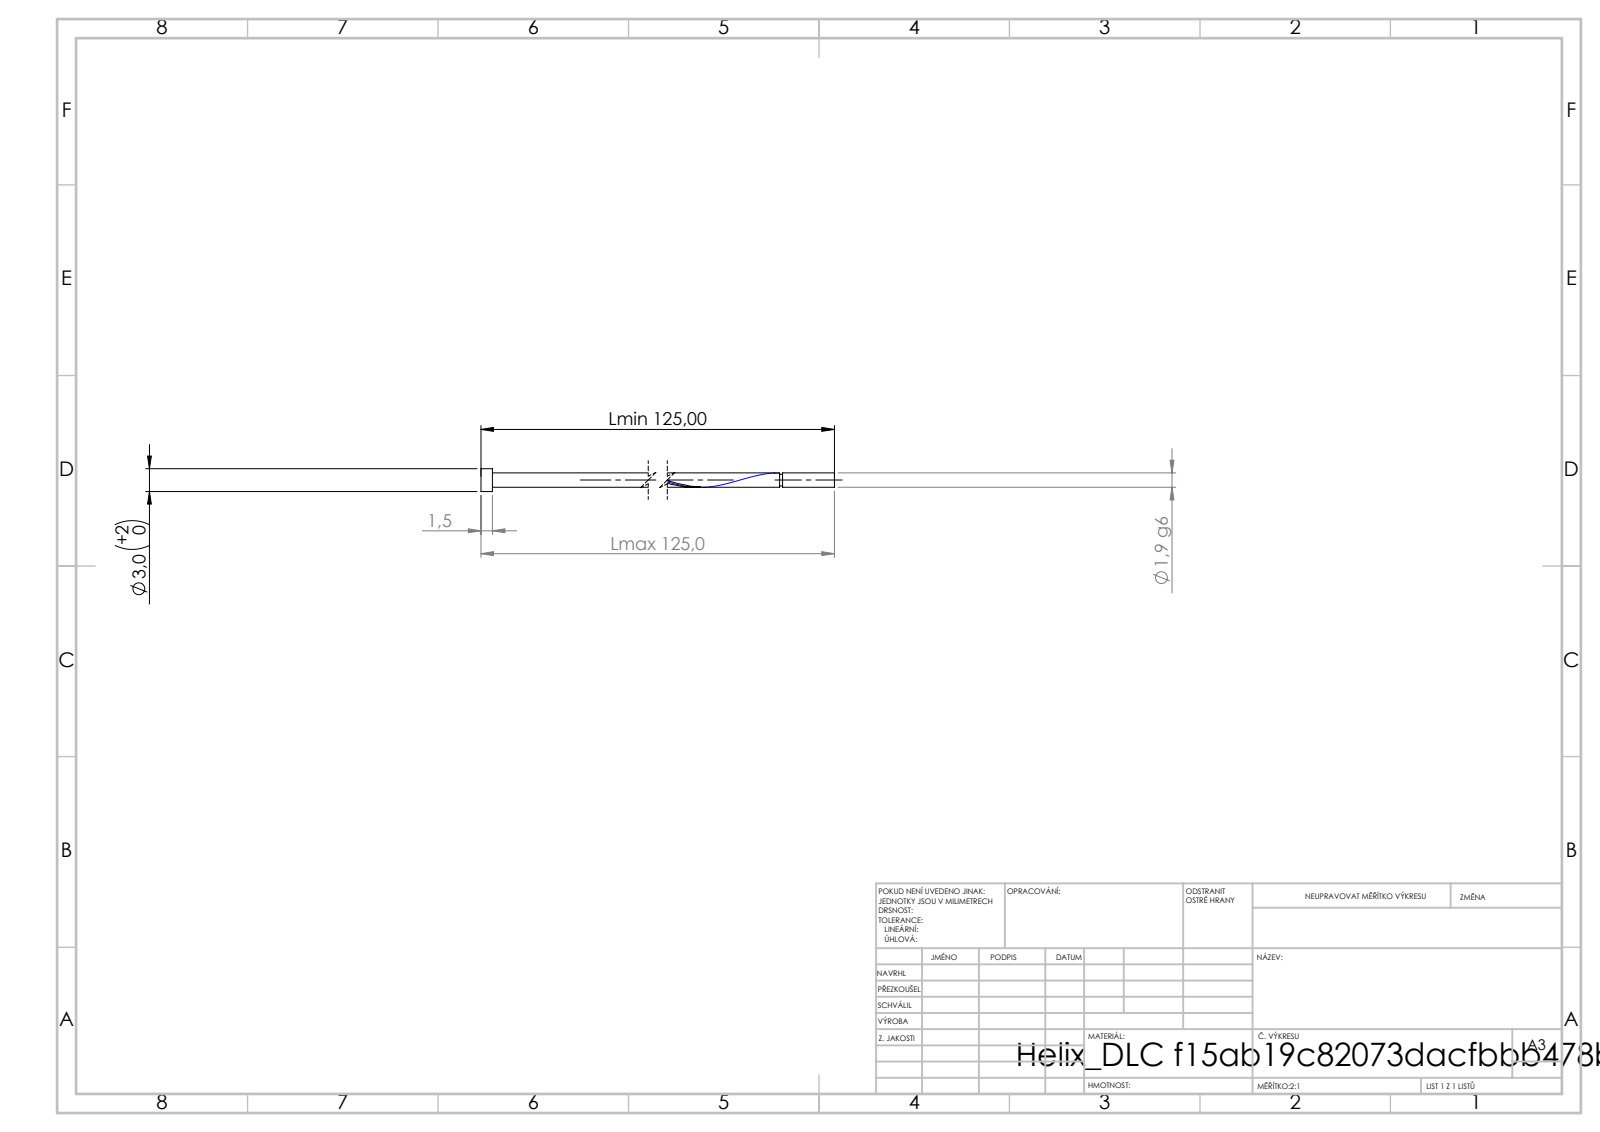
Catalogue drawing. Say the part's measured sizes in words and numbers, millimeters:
Its 3-D file was written by "SolidWorks 2019 (CONFIG_CONTROL_DESIGN)". It is 1 solid with 16 faces: 6 planar, 9 cylindrical and 1 other. Overall it measures 125 by 3 by 3 millimeters. Its volume is 436 cubic millimeters and its surface area 1 028 square millimeters. Round bosses or shafts: 1 of diameter 3, 1 of diameter 1.9, 1 of diameter 1.52. The main face-to-face distances are 1.5, 125, 123.5, 118.19, 116.69, 6.81, 117.81, 116.31, 0.38, 7.19.
